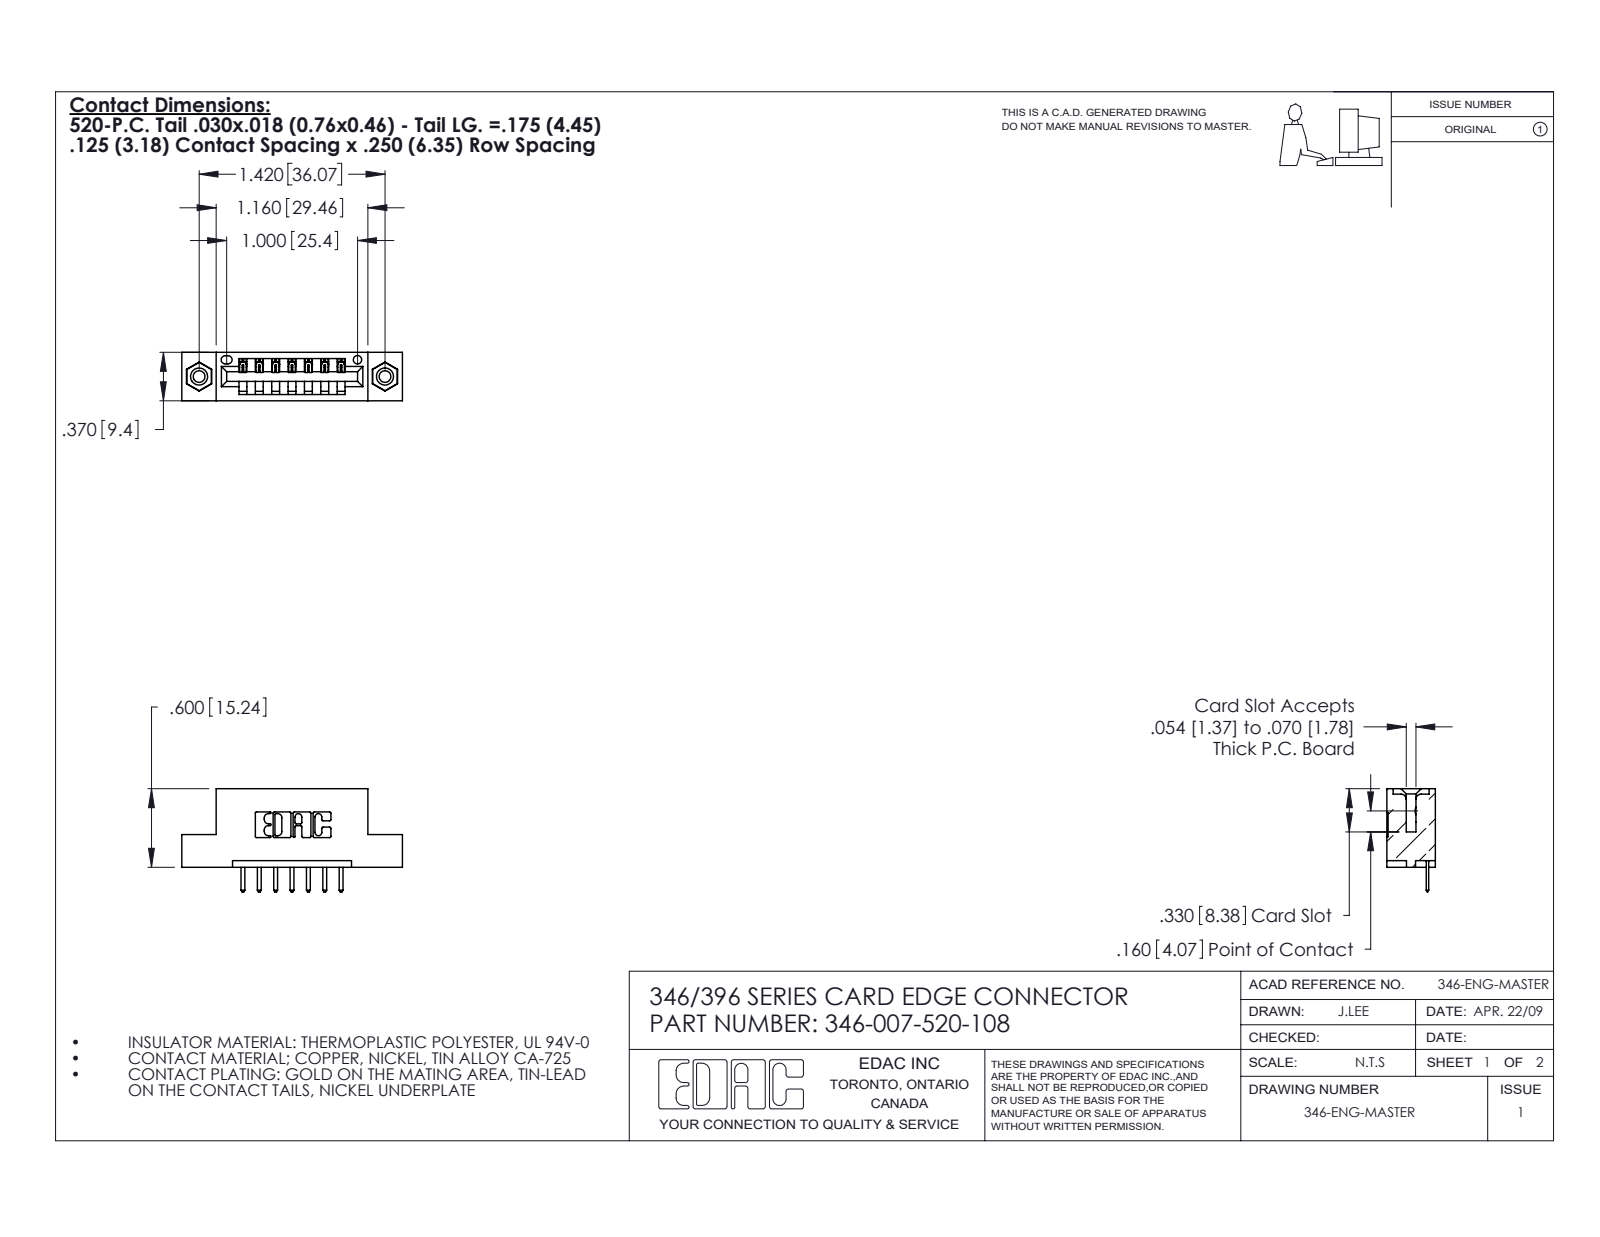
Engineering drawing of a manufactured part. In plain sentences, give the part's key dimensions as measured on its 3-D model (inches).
The part is named "345-250-001_345-250-003-102; 346-007-520-108; 346 Part_Flush Mounting Lugs - 0.156 Dia-TI; 345-292-001_345-293-120". Its 3-D file was written by "SolidWorks 2020 (CONFIG_CONTROL_DESIGN)". It is 10 solids with 616 faces: 402 planar, 198 cylindrical and 16 other. Overall it measures 1.685 by 0.788 by 0.37 inches. Its volume is 0.234 cubic inches and its surface area 6.762 square inches. Round holes: 2 of diameter 0.089, 2 of diameter 0.125, 2 of diameter 0.156, 1 of diameter 0.064. Round bosses or shafts: 2 of diameter 0.155. Partial cylindrical surfaces (rounded edges, fillets, slot ends): 22 of radius 0.01, 16 of radius 0.01, 14 of radius 0.006, 6 of radius 0.007, 6 of radius 0.031, 3 of radius 0.026, 2 of radius 0.031, 2 of radius 0.04. The main face-to-face distances are 0.25, 0.37, 0.048, 0.322, 0.148, 0.222, 0.1, 0.174, 0.125, 0.185. The hole center spacings are 0.246, 1.217, 1.42.
